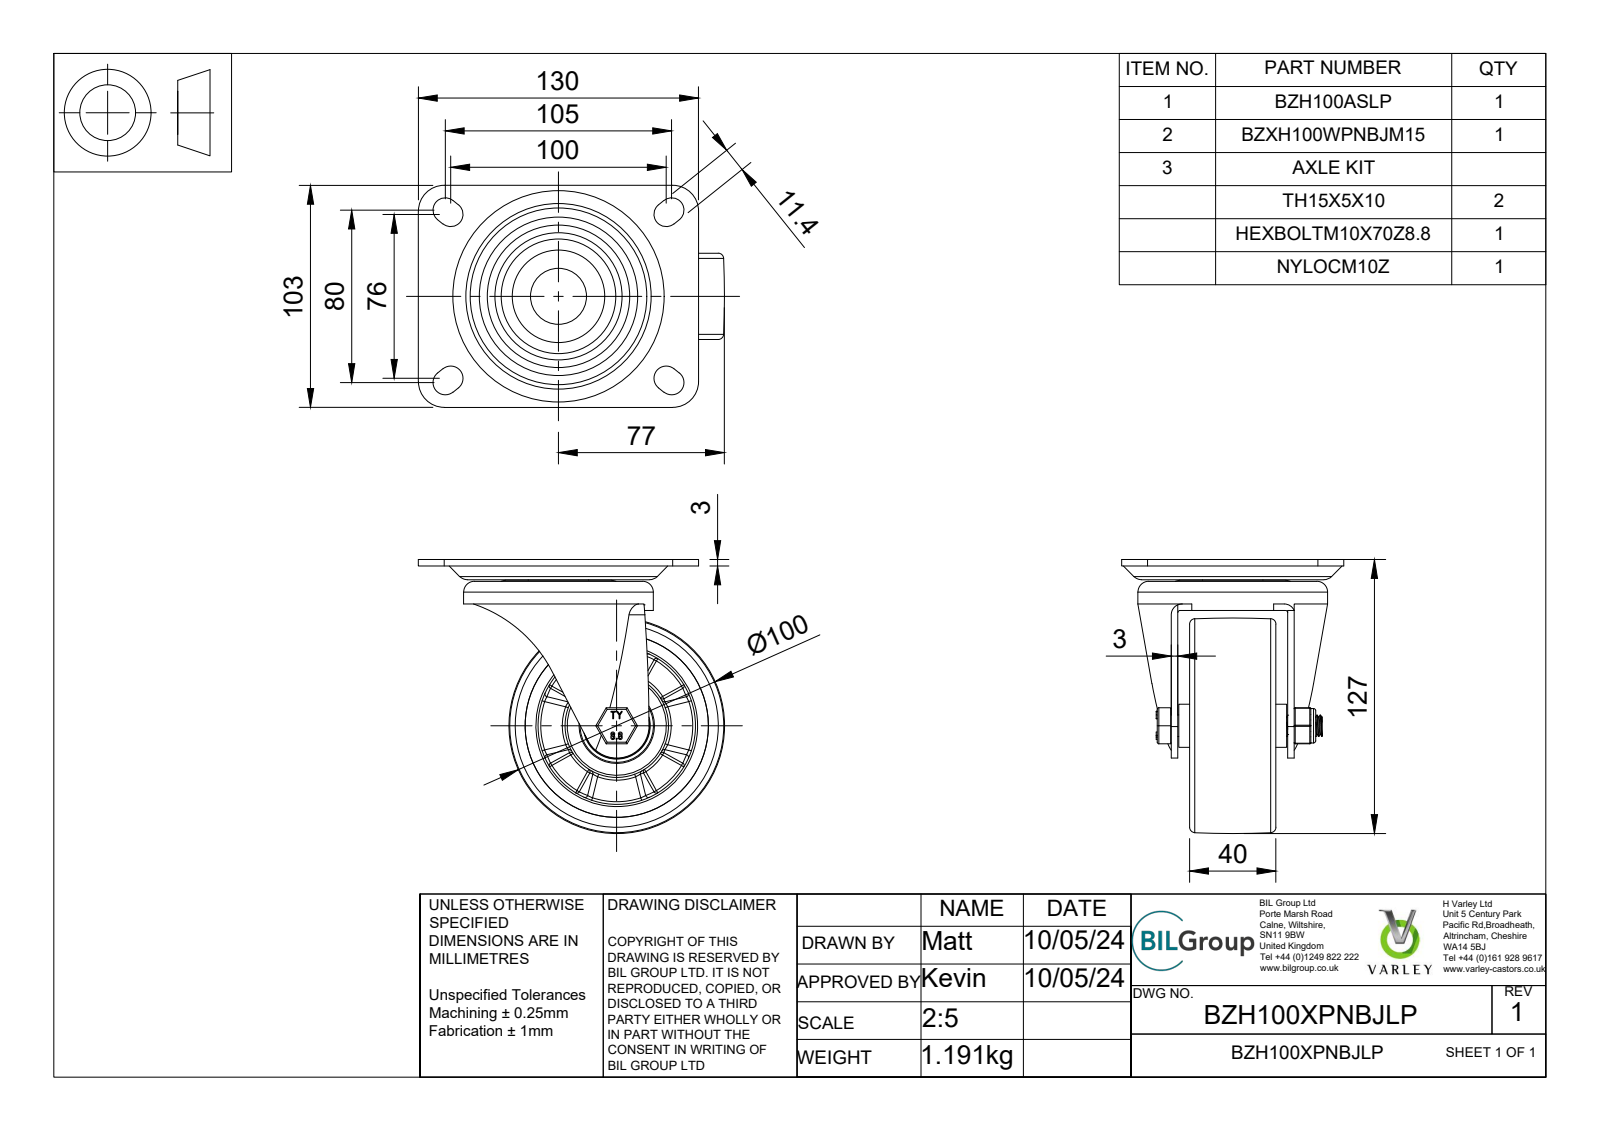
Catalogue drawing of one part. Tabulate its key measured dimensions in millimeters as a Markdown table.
| quantity | value |
| --- | --- |
| part name | BZH100XPNBJLP v3; BZH100ASLP v1; ZINC PLATED PRESSED STEEL FORK; ZINC PLATED PRESSED STEEL TOP PLATE (+7 more) |
| STEP written by | Autodesk Translation Framework v12.20.1.177 (AUTOMOTIVE_DESIGN) |
| units | millimeters |
| bodies | 36 solids, 1193 faces (401 planar, 195 cylindrical, 597 other) |
| overall size | 142 × 127.13 × 103 |
| volume | 326 162 mm³ |
| surface area | 156 235 mm² |
| round holes (diameter × count) | 30 × 2, 10 × 1, 10.5 × 1, 12 × 1, 15 × 1, 22.5 × 1, 31 × 1, 32 × 1, 35 × 1, 73 × 1, 82 × 1, 85 × 1 |
| round bosses / shafts (diameter × count) | 88 × 1, 48 × 1, 36 × 1, 30.5 × 1, 28 × 1, 26 × 1, 23 × 1, 22 × 1 |
| partial cylindrical surfaces (radius × count) | 0.5 × 18, 5.7 × 8, 0.75 × 6, 12 × 5, 1 × 2, 5 × 2, 13.75 × 1, 64.34 × 1 |
| main face-to-face distances | 3, 40, 10.5, 5, 0.5, 5.5, 29, 35, 30, 8.5 |
